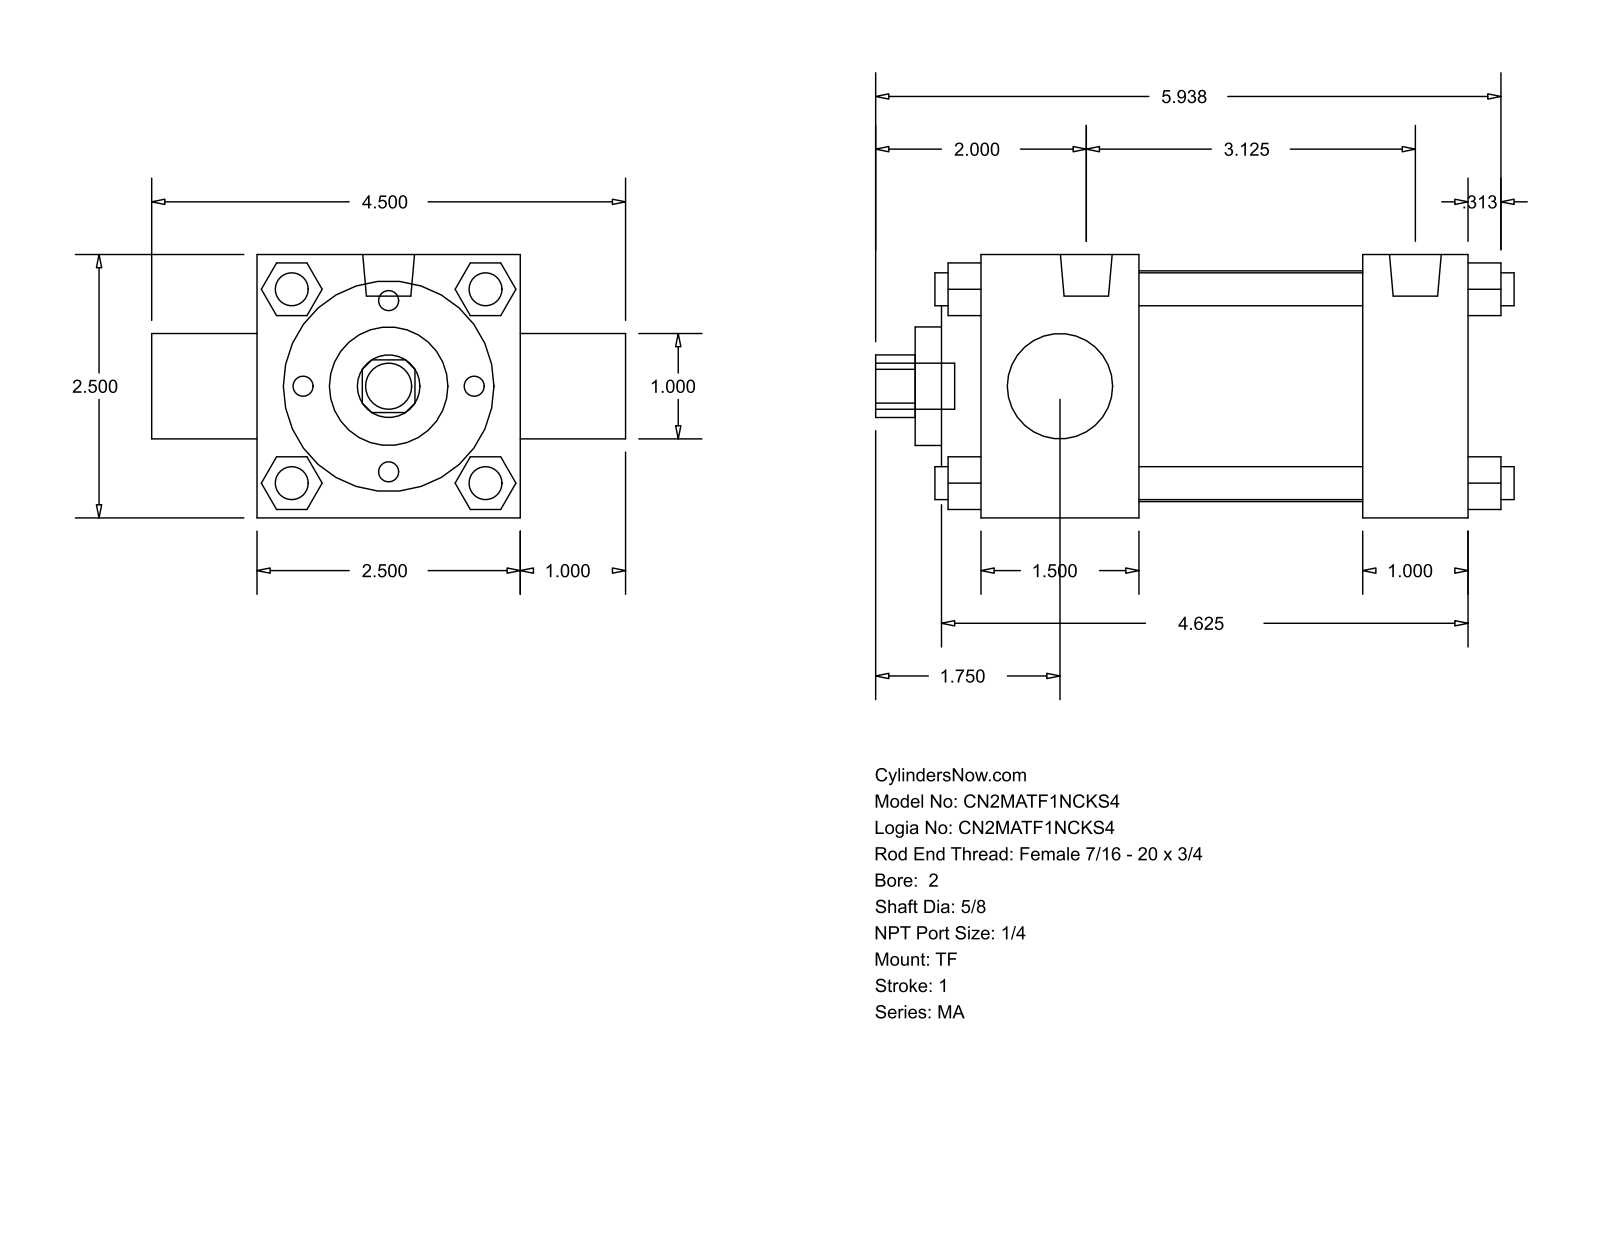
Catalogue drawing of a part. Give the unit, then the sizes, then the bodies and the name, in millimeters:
Units: millimetres
Overall size (bounding box): 153.99 × 114.3 × 63.5
Round holes (diameter × count): ⌀15.88 ×1, ⌀25.4 ×1, ⌀28.57 ×1, ⌀50.8 ×1, ⌀55.63 ×1
Round bosses / shafts (diameter × count): ⌀7.94 ×7, ⌀12.49 ×2, ⌀11.11 ×1
Partial cylindrical surfaces — rounded edges, fillets, slot ends (radius × count): R7.54 ×1
Main face-to-face distances: 63.5, 53.97, 38.1, 12.7, 9.52, 117.48, 92.07, 79.38, 25.41, 47.62
Bodies: 0 solids, 122 faces (93 planar, 29 cylindrical, 0 other)
Part name (STEP PRODUCT): MA_TF__0200_0.625
STEP written by: GSSL Pune (CONFIG_CONTROL_DESIGN)
